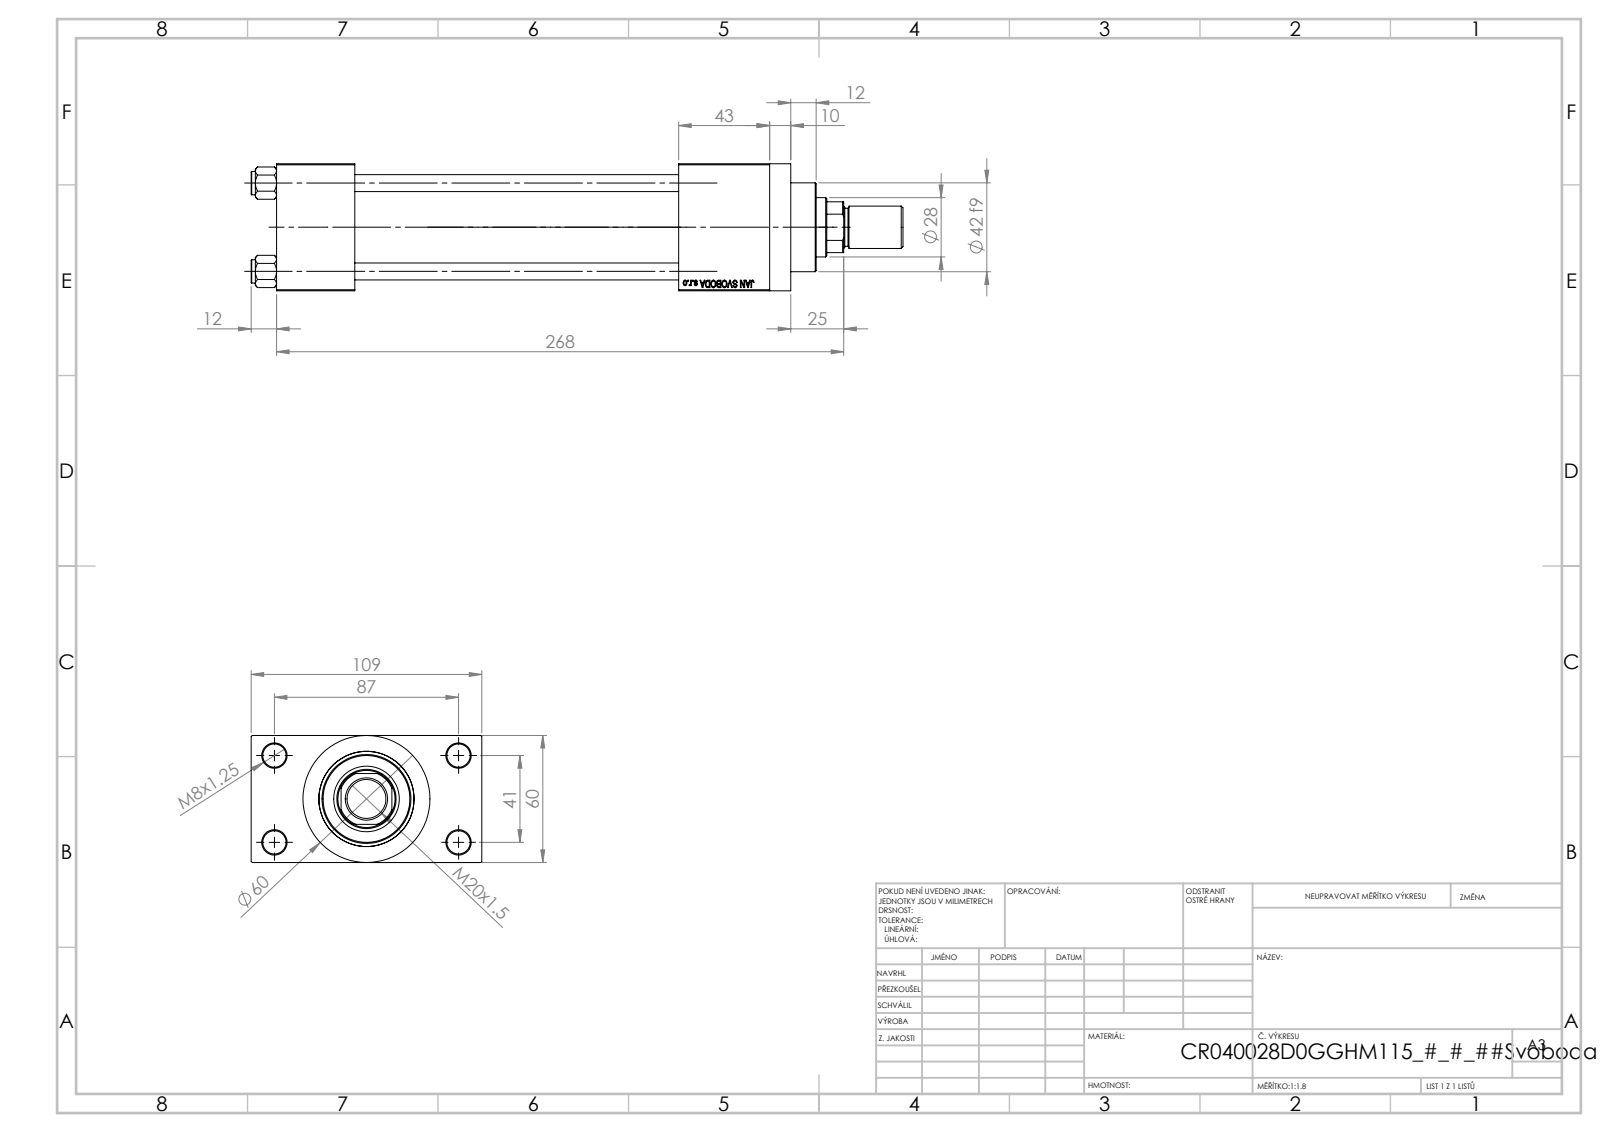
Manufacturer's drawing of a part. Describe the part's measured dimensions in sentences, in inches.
The part is named "ROD_END_AH; V215CR_VCP_D; NUT_M5_D; V215_VC_A (+2 more)". Its 3-D file was written by "SolidWorks 2019 (CONFIG_CONTROL_DESIGN)". It is 12 solids with 1119 faces: 502 planar, 93 cylindrical and 524 other. Overall it measures 12.126 by 4.291 by 2.362 inches. Its volume is 40.21 cubic inches and its surface area 269.4 square inches. Round holes: 4 of diameter 0.315, 4 of diameter 0.433, 2 of diameter 0.276, 2 of diameter 0.656, 2 of diameter 0.945, 1 of diameter 0.728, 1 of diameter 1.102, 1 of diameter 1.22, 1 of diameter 1.575, 1 of diameter 1.772. Round bosses or shafts: 4 of diameter 0.433, 1 of diameter 2.362, 1 of diameter 1.811, 1 of diameter 1.654, 1 of diameter 0.787, 1 of diameter 0.709. Partial cylindrical surfaces (rounded edges, fillets, slot ends): 1 of radius 0.531. The main face-to-face distances are 2.362, 0.965, 3.327, 6.024, 1.457, 7.48, 9.173, 7.717, 1.693, 4.291. The hole center spacings are 0.892, 1.161, 1.642, 1.856, 1.893, 2.533, 3.011, 1.614.
